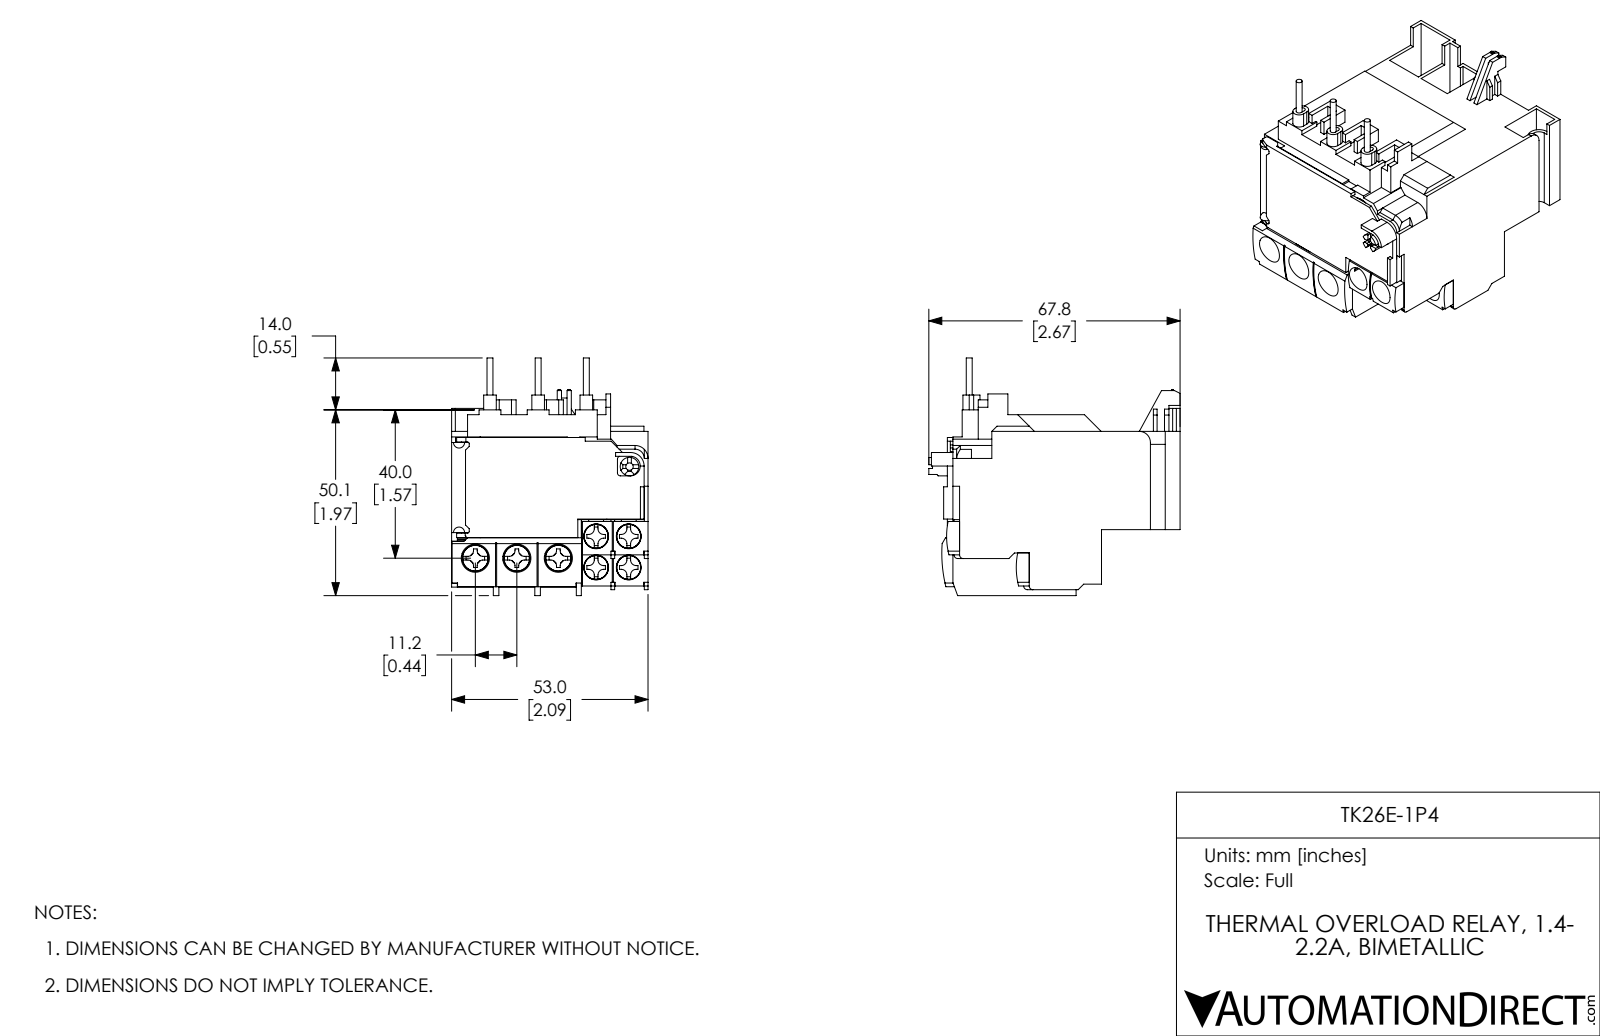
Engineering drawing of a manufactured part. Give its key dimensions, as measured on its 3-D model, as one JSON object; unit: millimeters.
{"part_name": "TK26E-1P4", "step_written_by": "SolidWorks 2017 (AUTOMOTIVE_DESIGN)", "units": "millimeters", "bodies": {"solids": 38, "faces": 1480, "planar": 1225, "cylindrical": 220, "other": 35}, "overall_size": [67.8, 64.1, 53], "volume_mm3": 99940, "surface_area_mm2": 38810, "round_holes": [[3.5, 4], [3.6, 4], [6.7, 4], [4, 3], [4.1, 3], [7.6, 3], [1, 1], [2, 1], [5, 1], [11, 1]], "round_bosses_or_shafts": [[6.6, 4], [1.6, 3], [6, 1]], "partial_cylinders_radius": [[1.5, 28], [1, 8], [0.5, 6], [1.7, 6], [0.8, 5], [1.2, 4], [4.3, 4], [4.8, 3]], "face_to_face_distances": [1, 9, 1.5, 12, 53, 2, 10, 11, 8.7, 0.7], "hole_center_spacings": [8.4, 8.8, 11.2, 12.2, 9.6, 10.5, 11.8, 18.8]}
